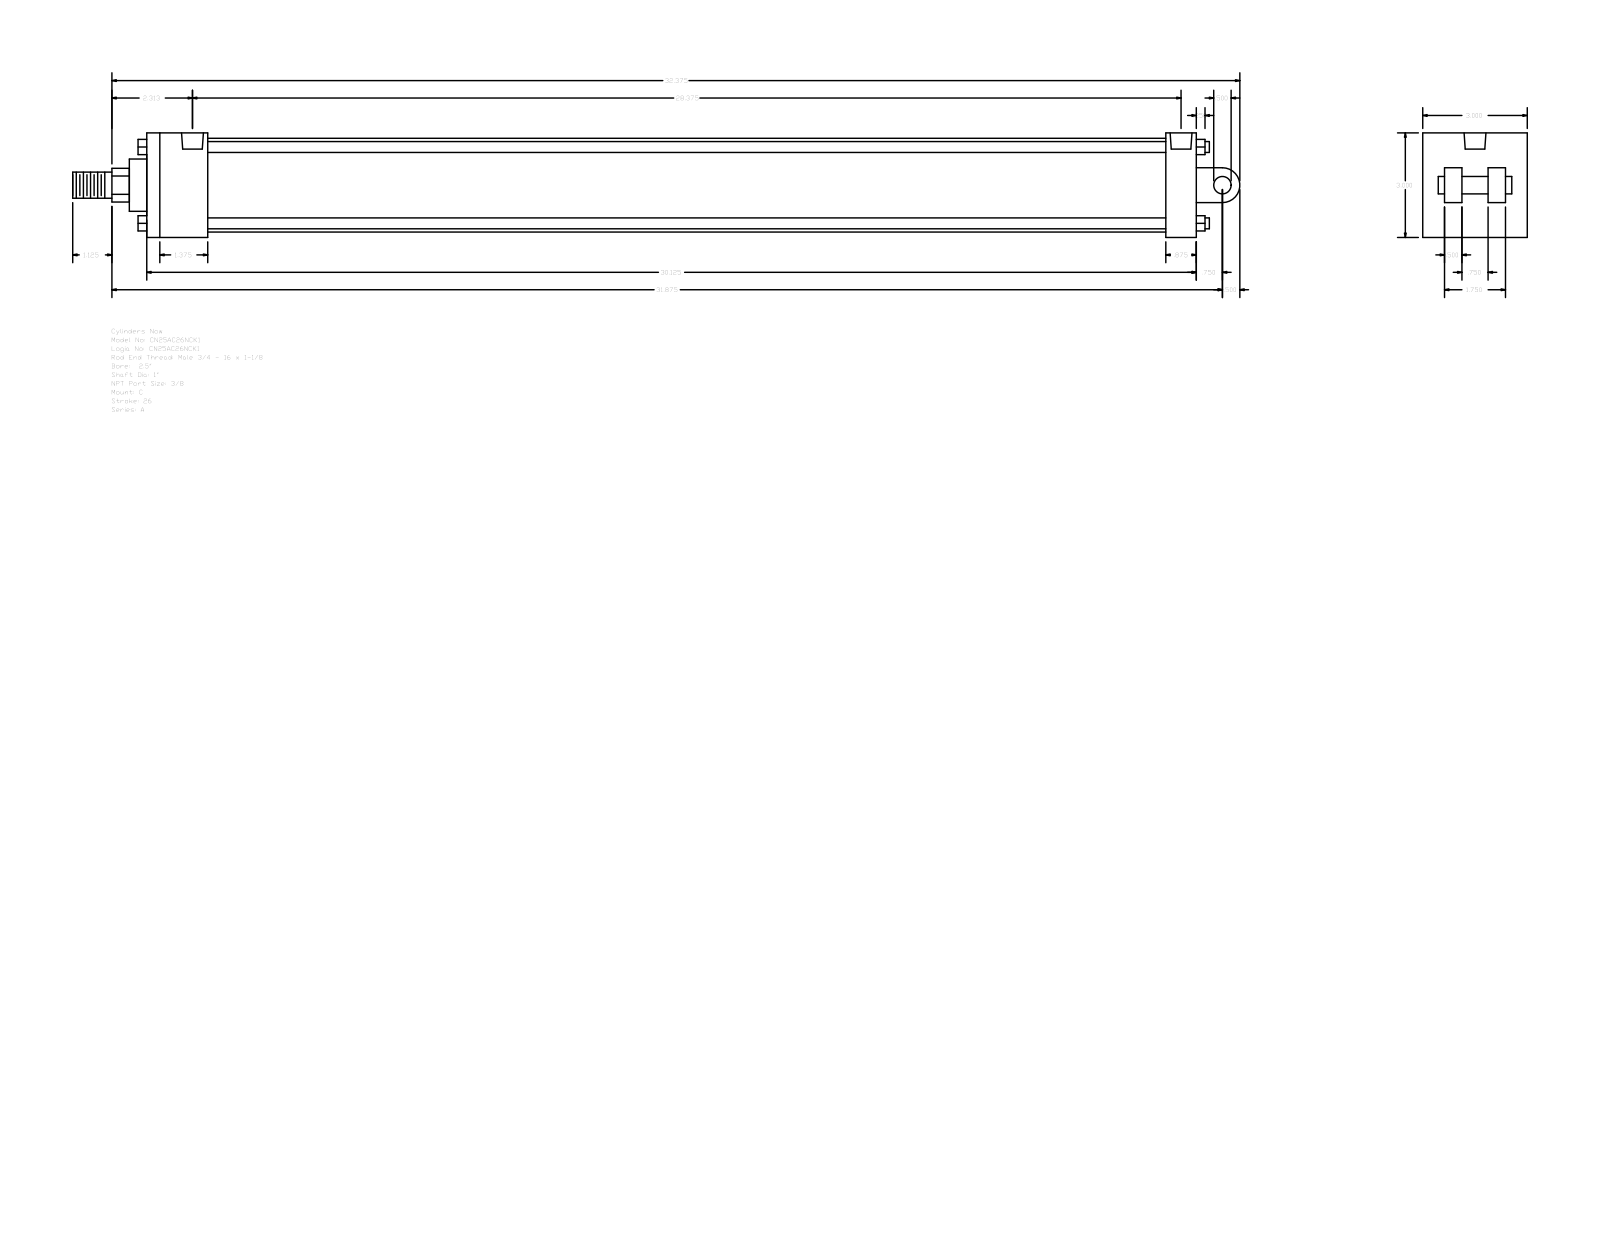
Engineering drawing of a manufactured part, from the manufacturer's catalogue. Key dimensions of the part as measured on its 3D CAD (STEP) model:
Part name (STEP PRODUCT): A_C__0250_1
STEP written by: GSSL Pune (CONFIG_CONTROL_DESIGN)
Units: millimetres
Bodies: 0 solids, 135 faces (102 planar, 33 cylindrical, 0 other)
Overall size (bounding box): 850.9 × 76.2 × 76.2
Round holes (diameter × count): ⌀5.56 ×4, ⌀15.93 ×2
Round bosses / shafts (diameter × count): ⌀7.94 ×4, ⌀68.33 ×1, ⌀38.1 ×1, ⌀25.4 ×1, ⌀19.05 ×1, ⌀12.7 ×1
Partial cylindrical surfaces — rounded edges, fillets, slot ends (radius × count): R12.29 ×1, R12.7 ×1
Main face-to-face distances: 76.2, 765.18, 12.7, 44.45, 742.95, 698.5, 720.73, 22.23, 15.87, 25.4
Hole centre spacings: 2.38, 723.1, 725.48, 720.72
